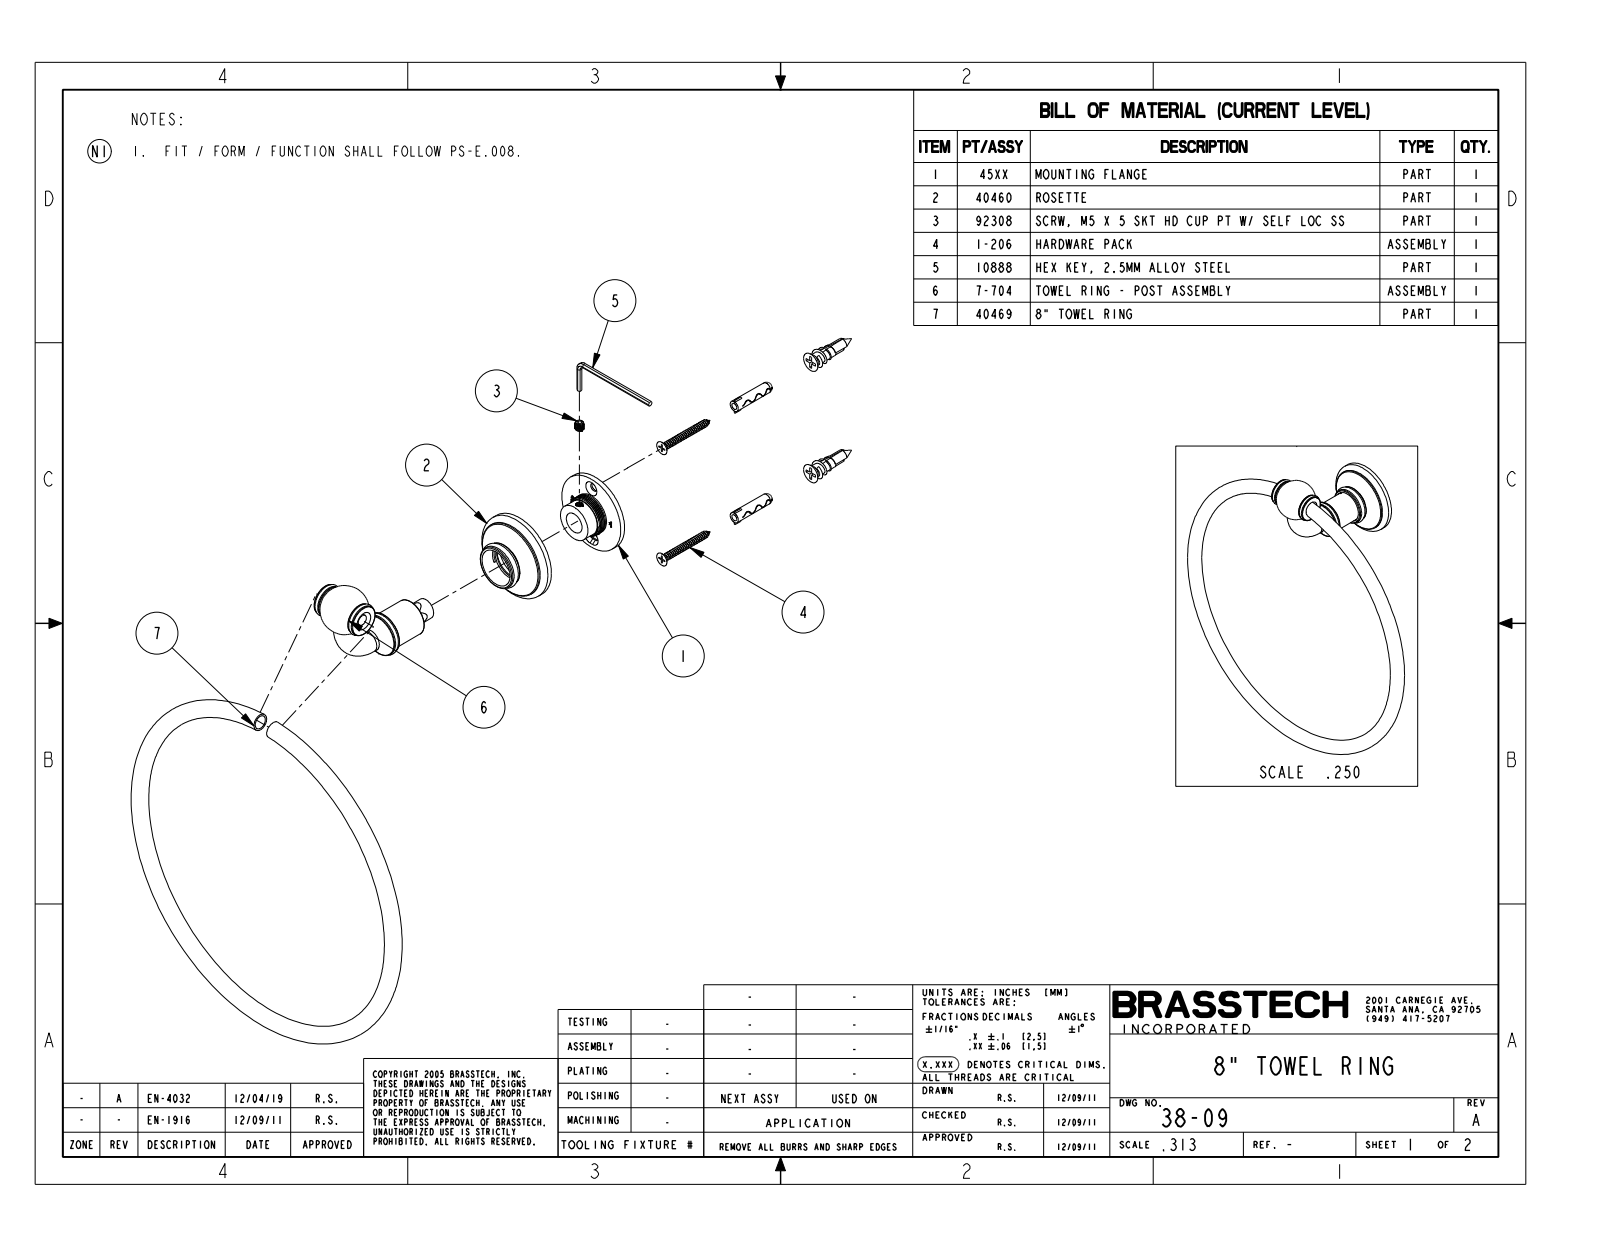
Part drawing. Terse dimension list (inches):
name: 38-09_WEB
written by: PRO/ENGINEER BY PARAMETRIC TECHNOLOGY CORPORATION, 2009300 (CONFIG_CONTROL_DESIGN)
unit: in
bodies: 0 solids, 76 faces (8 planar, 24 cylindrical, 44 other)
size: 8.602 × 8.26 × 3.246
bosses: 1× ⌀2, 1× ⌀1.76, 1× ⌀1, 1× ⌀0.965, 1× ⌀0.845, 1× ⌀0.709, 1× ⌀0.5
face distances: 0.148, 1.046, 0.72, 1.478, 0.758, 0.898, 1.194
